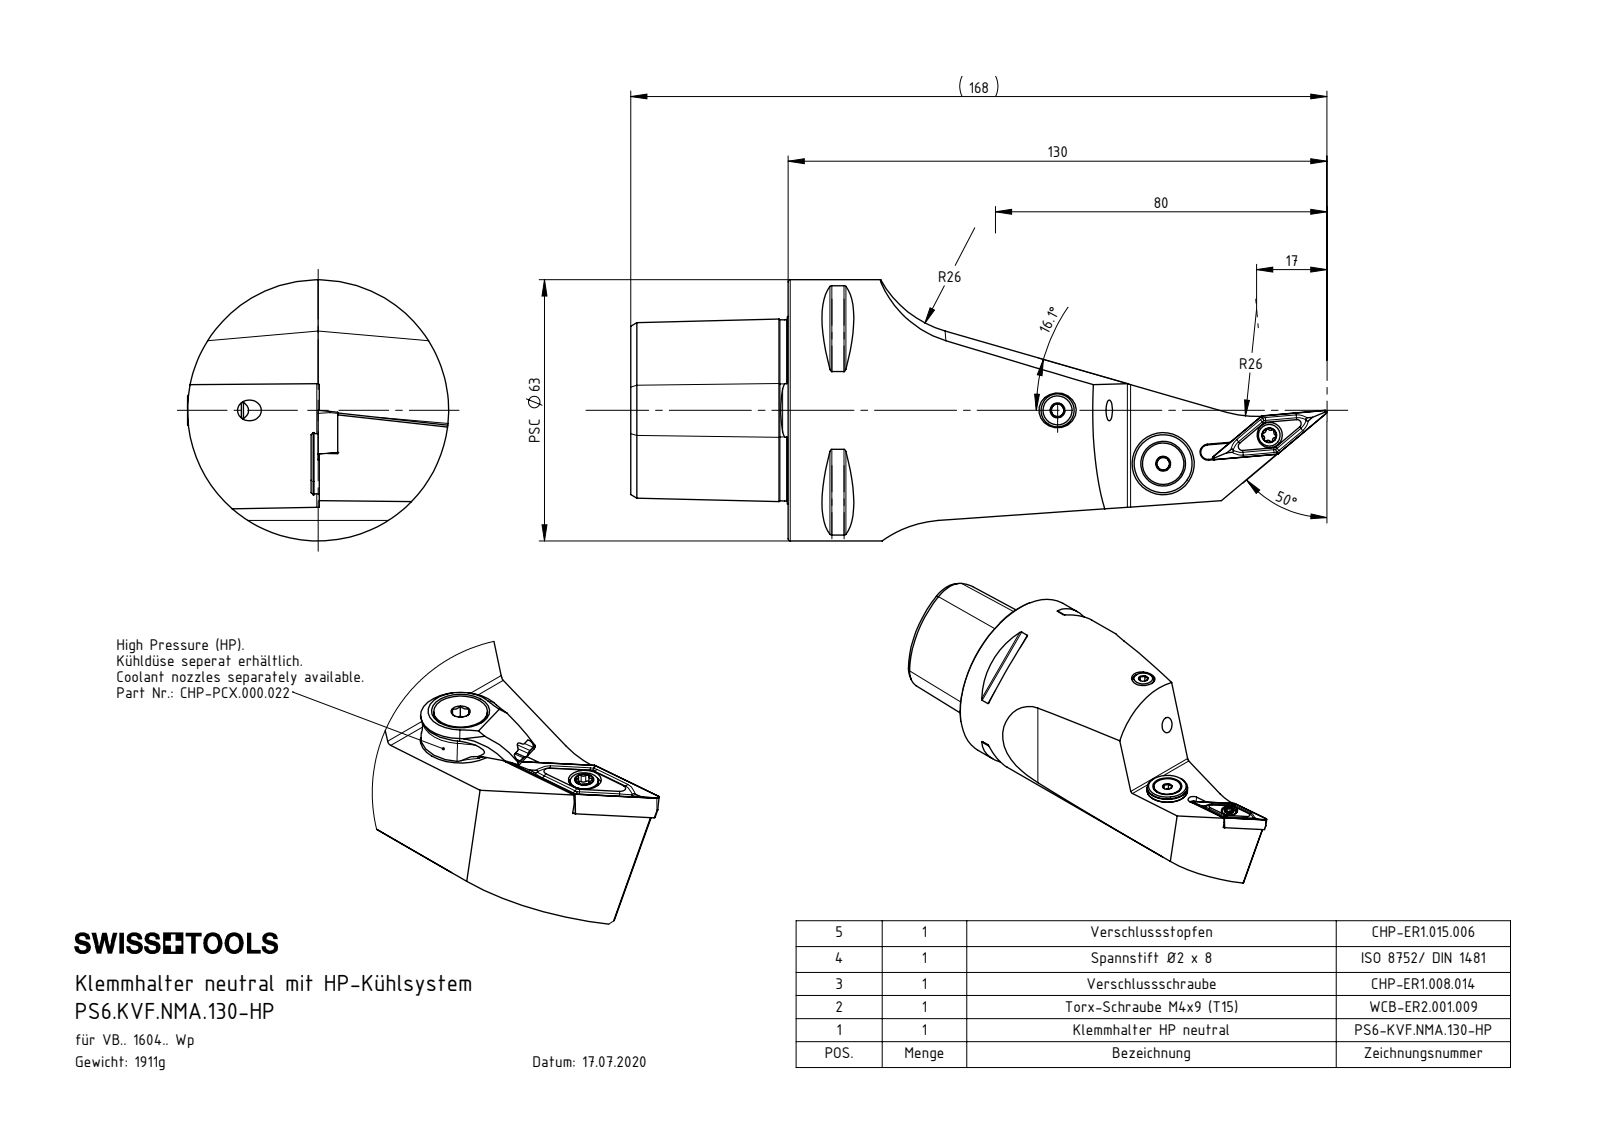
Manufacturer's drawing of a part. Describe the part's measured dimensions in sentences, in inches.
The part is named "CHP-ER1.015.006_A; PS6.KVF.NMA.130-HP; CHP-ER1.008.014_A; PS6-KVF.NMA.130-HP_A (+6 more)". Its 3-D file was written by "SolidWorks 2017 (AUTOMOTIVE_DESIGN)". It is 8 solids with 275 faces: 92 planar, 66 cylindrical and 117 other. Overall it measures 6.614 by 2.488 by 2.48 inches. Its volume is 14.89 cubic inches and its surface area 60.76 square inches. Round holes: 2 of diameter 0.165, 2 of diameter 0.197, 1 of diameter 0.047, 1 of diameter 0.079, 1 of diameter 0.098, 1 of diameter 0.118, 1 of diameter 0.13, 1 of diameter 0.157, 1 of diameter 0.173, 1 of diameter 0.205, 1 of diameter 0.24, 1 of diameter 0.276. Round bosses or shafts: 1 of diameter 2.48, 1 of diameter 0.591, 1 of diameter 0.528, 1 of diameter 0.394, 1 of diameter 0.315, 1 of diameter 0.217, 1 of diameter 0.207, 1 of diameter 0.197. Partial cylindrical surfaces (rounded edges, fillets, slot ends): 8 of radius 0.02, 6 of radius 0.013, 6 of radius 0.023, 4 of radius 1.024, 2 of radius 0.006, 2 of radius 0.031, 1 of radius 0.069, 1 of radius 0.236. The main face-to-face distances are 1.496, 0.98, 4.528, 3.031, 0.176, 0.177, 1.063, 0.433, 3.465, 2.197. The hole center spacings are 0.177, 0.915, 0.919, 1.043, 1.048, 1.083, 3.131, 3.212.
